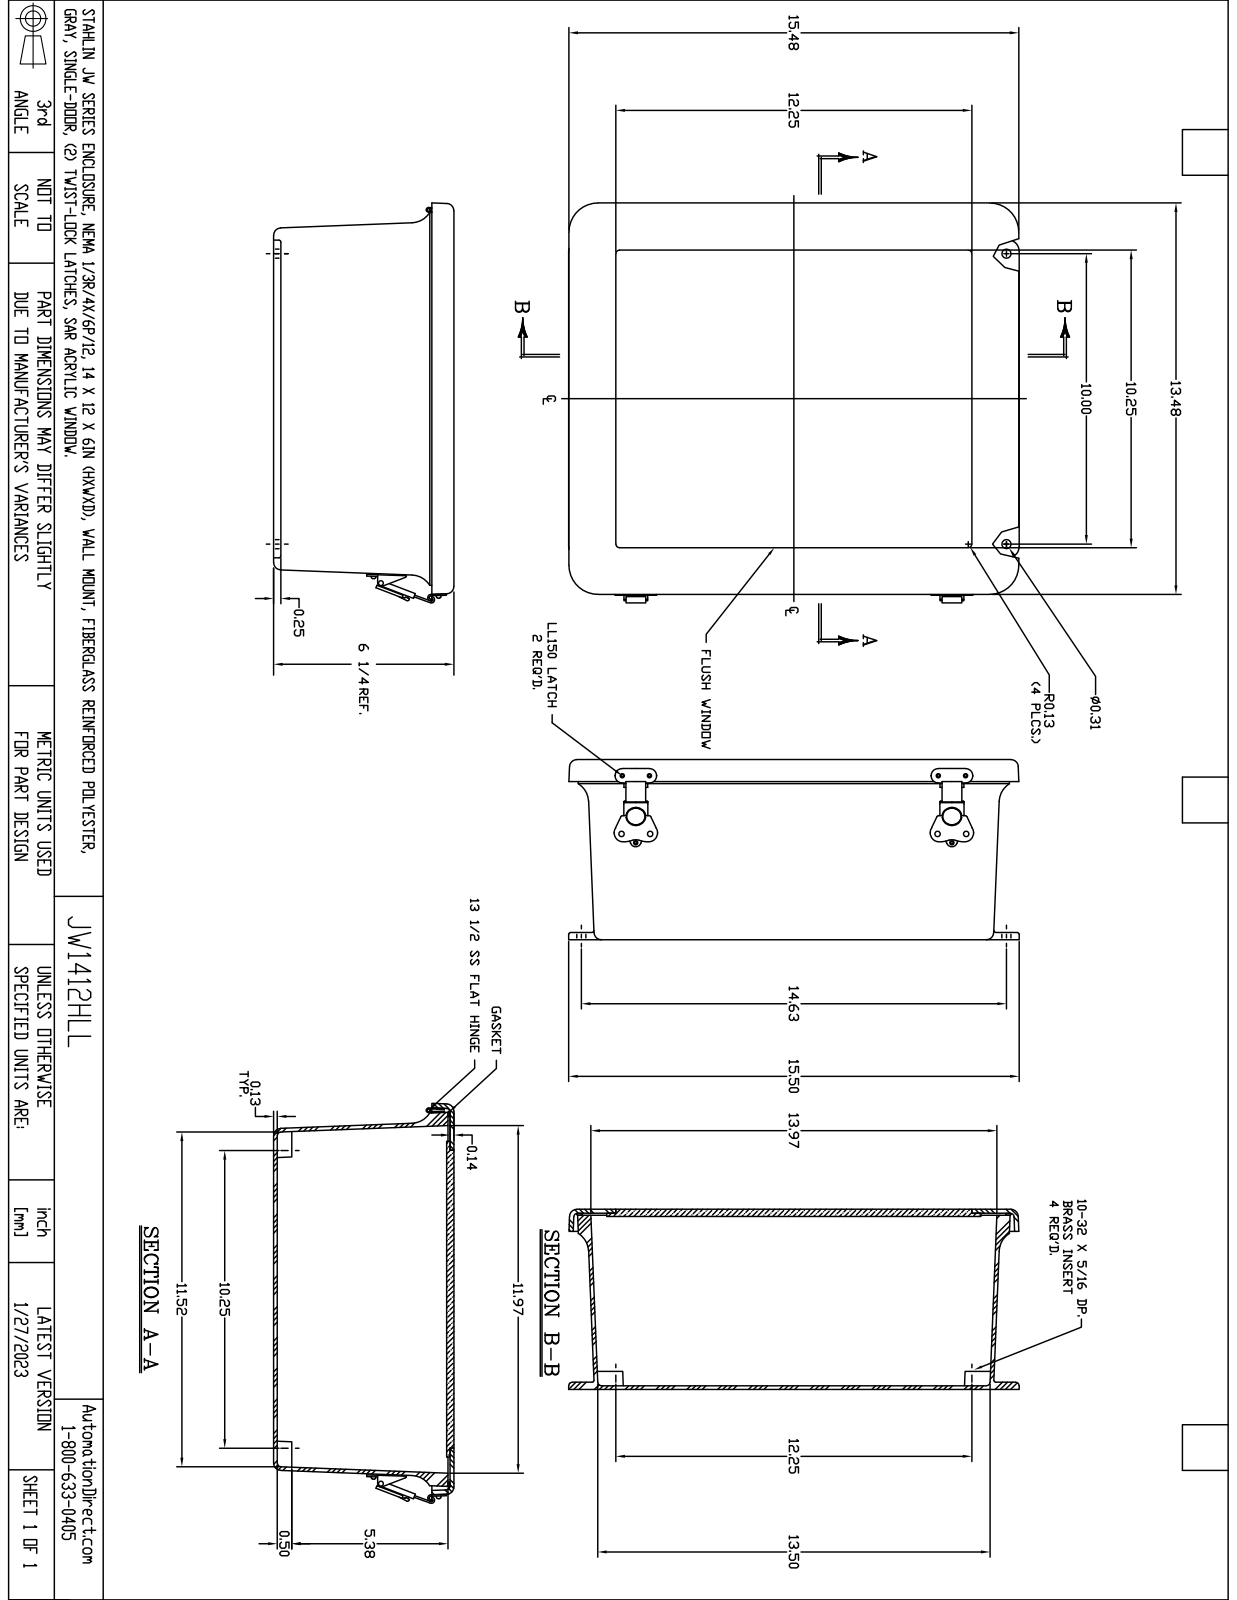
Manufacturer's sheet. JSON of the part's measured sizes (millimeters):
{"part_name": "MW1412HLL", "step_written_by": "SolidWorks 2018 (AUTOMOTIVE_DESIGN)", "units": "millimeters", "bodies": {"solids": 51, "faces": 1235, "planar": 558, "cylindrical": 484, "other": 193}, "overall_size": [393.7, 348.1, 157.5], "volume_mm3": 2125000, "surface_area_mm2": 1062000, "round_holes": [[3.6, 18], [3.3, 10], [3.9, 8], [3.3, 4], [4, 4], [4.2, 4], [5, 4], [5.5, 4], [3, 2], [3.5, 2], [4.6, 2], [4.6, 2]], "round_bosses_or_shafts": [[6.4, 18], [3.2, 12], [3.2, 6], [6.9, 4], [14.8, 2], [13.3, 2], [5.3, 2], [4.7, 2]], "partial_cylinders_radius": [[0.8, 20], [2, 19], [3.2, 16], [6.4, 16], [0.9, 8], [1, 8], [1.1, 8], [1.2, 8]], "face_to_face_distances": [3.2, 157.5, 6.4, 151.1, 154.3, 147.9, 3.2, 2.9, 154, 150.9], "hole_center_spacings": [82.6, 165.1, 276.4, 247.7, 6.4, 76.2, 15.6, 21]}
